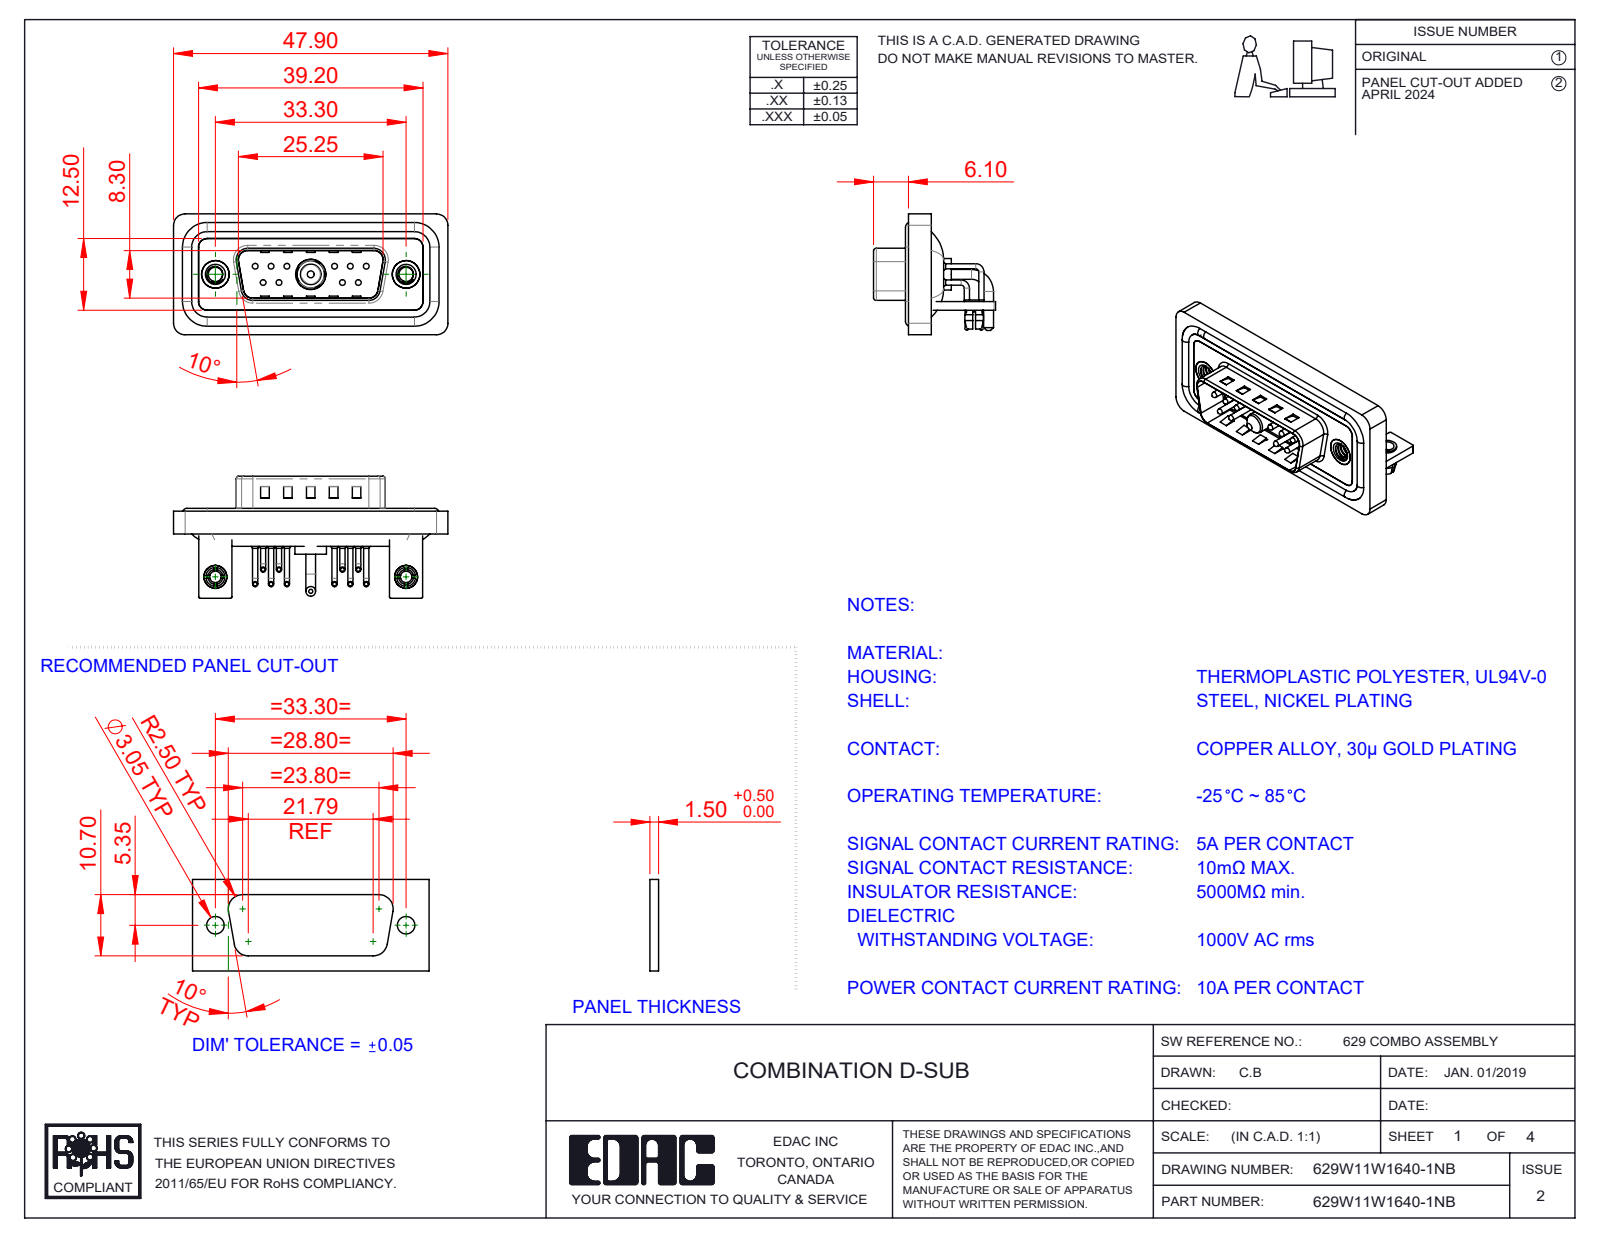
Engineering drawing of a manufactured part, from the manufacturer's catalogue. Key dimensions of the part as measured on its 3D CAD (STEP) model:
Part name (STEP PRODUCT): 629Combo Stabilizer Bracket; 629Combo Housing_11W1; 629W11W1640-1NB; 629Combo Shell Rear_15 Contacts (+7 more)
STEP written by: SolidWorks 2023 (CONFIG_CONTROL_DESIGN)
Units: millimetres
Bodies: 23 solids, 1733 faces (904 planar, 619 cylindrical, 210 other)
Overall size (bounding box): 47.9 × 21.3 × 21.1
Volume: 5 840 mm³ · Surface area: 10 028 mm²
Round holes (diameter × count): ⌀2 ×12, ⌀0.75 ×10, ⌀1.6 ×10, ⌀2.5 ×4, ⌀3.2 ×2, ⌀4 ×2, ⌀4.8 ×2, ⌀5 ×2, ⌀4.85 ×1, ⌀5.3 ×1
Round bosses / shafts (diameter × count): ⌀0.9 ×20, ⌀1.5 ×10, ⌀1 ×10, ⌀0.65 ×10, ⌀1.6 ×4, ⌀4.9 ×2, ⌀4 ×2, ⌀3.4 ×2
Partial cylindrical surfaces — rounded edges, fillets, slot ends (radius × count): R2 ×21, R1.5 ×18, R0.25 ×16, R1.01 ×10, R0.5 ×9, R1.6 ×8, R1 ×7, R0.6 ×4
Main face-to-face distances: 0.4, 0.8, 1.5, 2.9, 2.1, 1.1, 1.6, 1.2, 3.7, 4.1
Hole centre spacings: 3.16, 2.77, 13.85, 11.08, 16.62, 5.03, 5.04, 5.54
